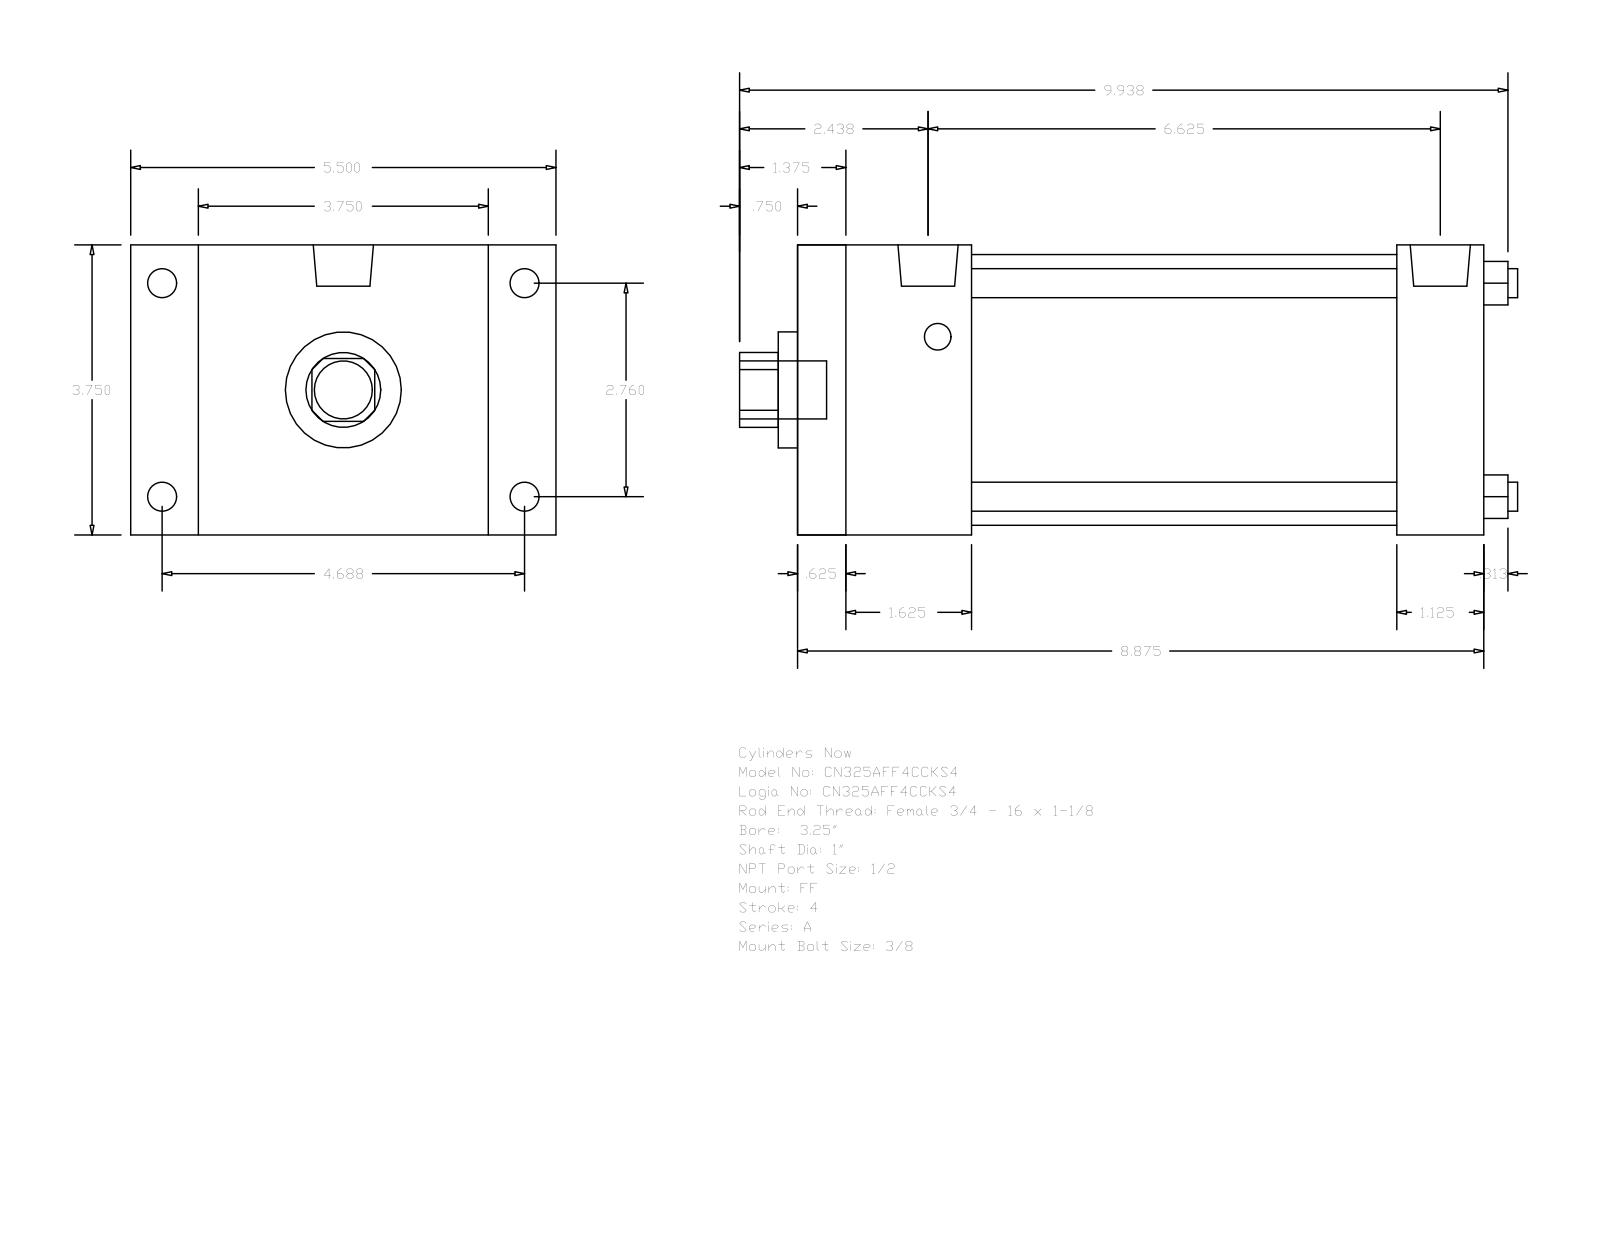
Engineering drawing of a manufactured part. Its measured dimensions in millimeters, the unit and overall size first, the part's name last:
Units: millimetres
Overall size (bounding box): 255.59 × 139.7 × 95.25
Round holes (diameter × count): ⌀9.53 ×4, ⌀25.4 ×1, ⌀38.1 ×1, ⌀88.9 ×1
Round bosses / shafts (diameter × count): ⌀9.53 ×4, ⌀8.73 ×4, ⌀19.77 ×2, ⌀19.05 ×1
Partial cylindrical surfaces — rounded edges, fillets, slot ends (radius × count): R12.29 ×1
Main face-to-face distances: 95.24, 225.42, 15.87, 139.7, 209.55, 22.23, 117.47, 28.57, 57.15, 196.85
Hole centre spacings: 49.57, 70.1, 99.14
Bodies: 0 solids, 92 faces (64 planar, 28 cylindrical, 0 other)
Part name (STEP PRODUCT): A_FF__0325_1
STEP written by: GSSL Pune (CONFIG_CONTROL_DESIGN)
